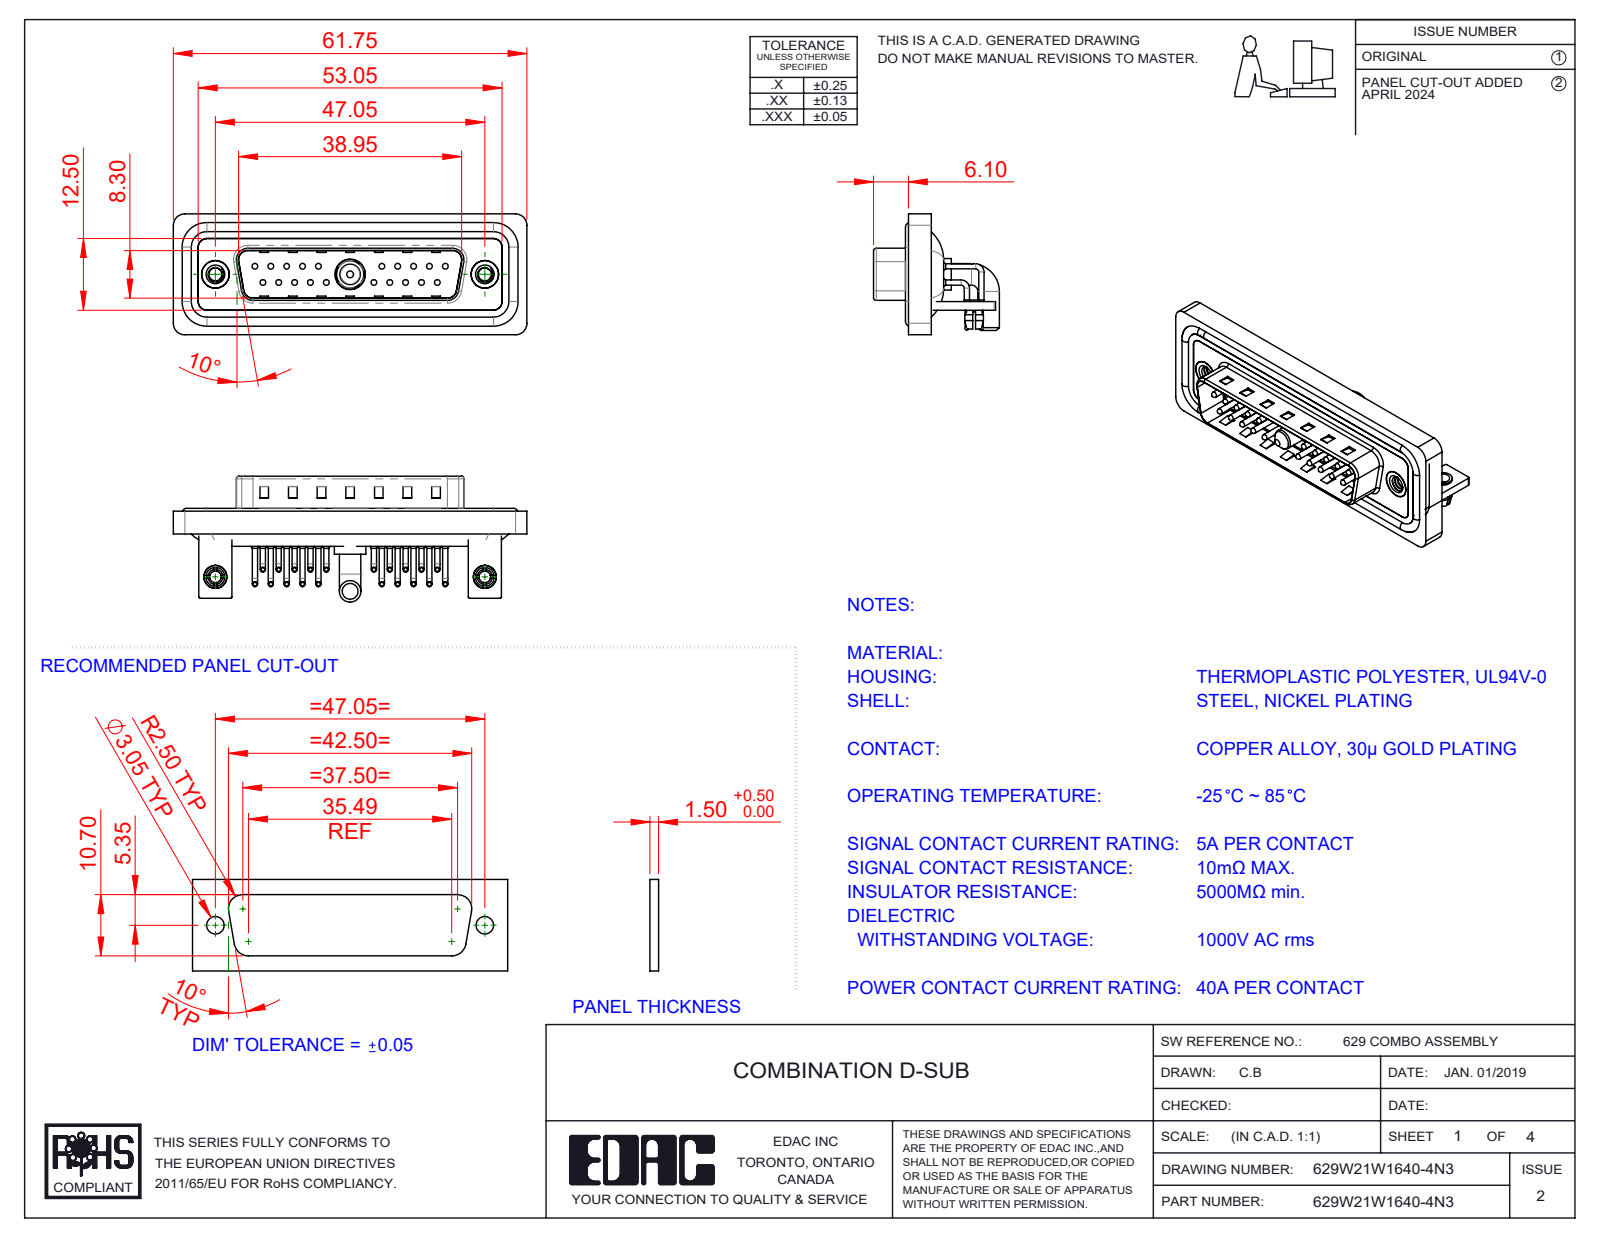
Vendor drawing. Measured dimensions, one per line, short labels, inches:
name: 629Combo Shell Rear_25 Contacts; 629Combo Stabilizer Bracket; 629Combo Waterproof Housing_25 Contacts; 629Combo Contact Row 2 (+7 more)
written by: SolidWorks 2023 (CONFIG_CONTROL_DESIGN)
unit: in
bodies: 33 solids, 2858 faces (1567 planar, 979 cylindrical, 312 other)
size: 2.431 × 0.865 × 0.831
volume: 0.476 in³; area: 21.02 in²
holes: 22× ⌀0.079, 20× ⌀0.03, 20× ⌀0.063, 2× ⌀0.089, 2× ⌀0.098, 2× ⌀0.126, 2× ⌀0.157, 2× ⌀0.189, 2× ⌀0.197, 1× ⌀0.191, 1× ⌀0.209
bosses: 40× ⌀0.035, 20× ⌀0.059, 20× ⌀0.039, 20× ⌀0.026, 4× ⌀0.063, 2× ⌀0.193, 2× ⌀0.157, 2× ⌀0.148
rounds: 20× R0.04, 19× R0.079, 18× R0.059, 16× R0.01, 9× R0.02, 8× R0.063, 4× R0.024, 4× R0.026
face distances: 0.016, 0.031, 0.083, 0.114, 0.059, 0.043, 0.161, 0.063, 0.177, 0.146
hole spacings: 0.124, 0.109, 0.218, 0.327, 0.198, 0.763, 0.826, 0.872
